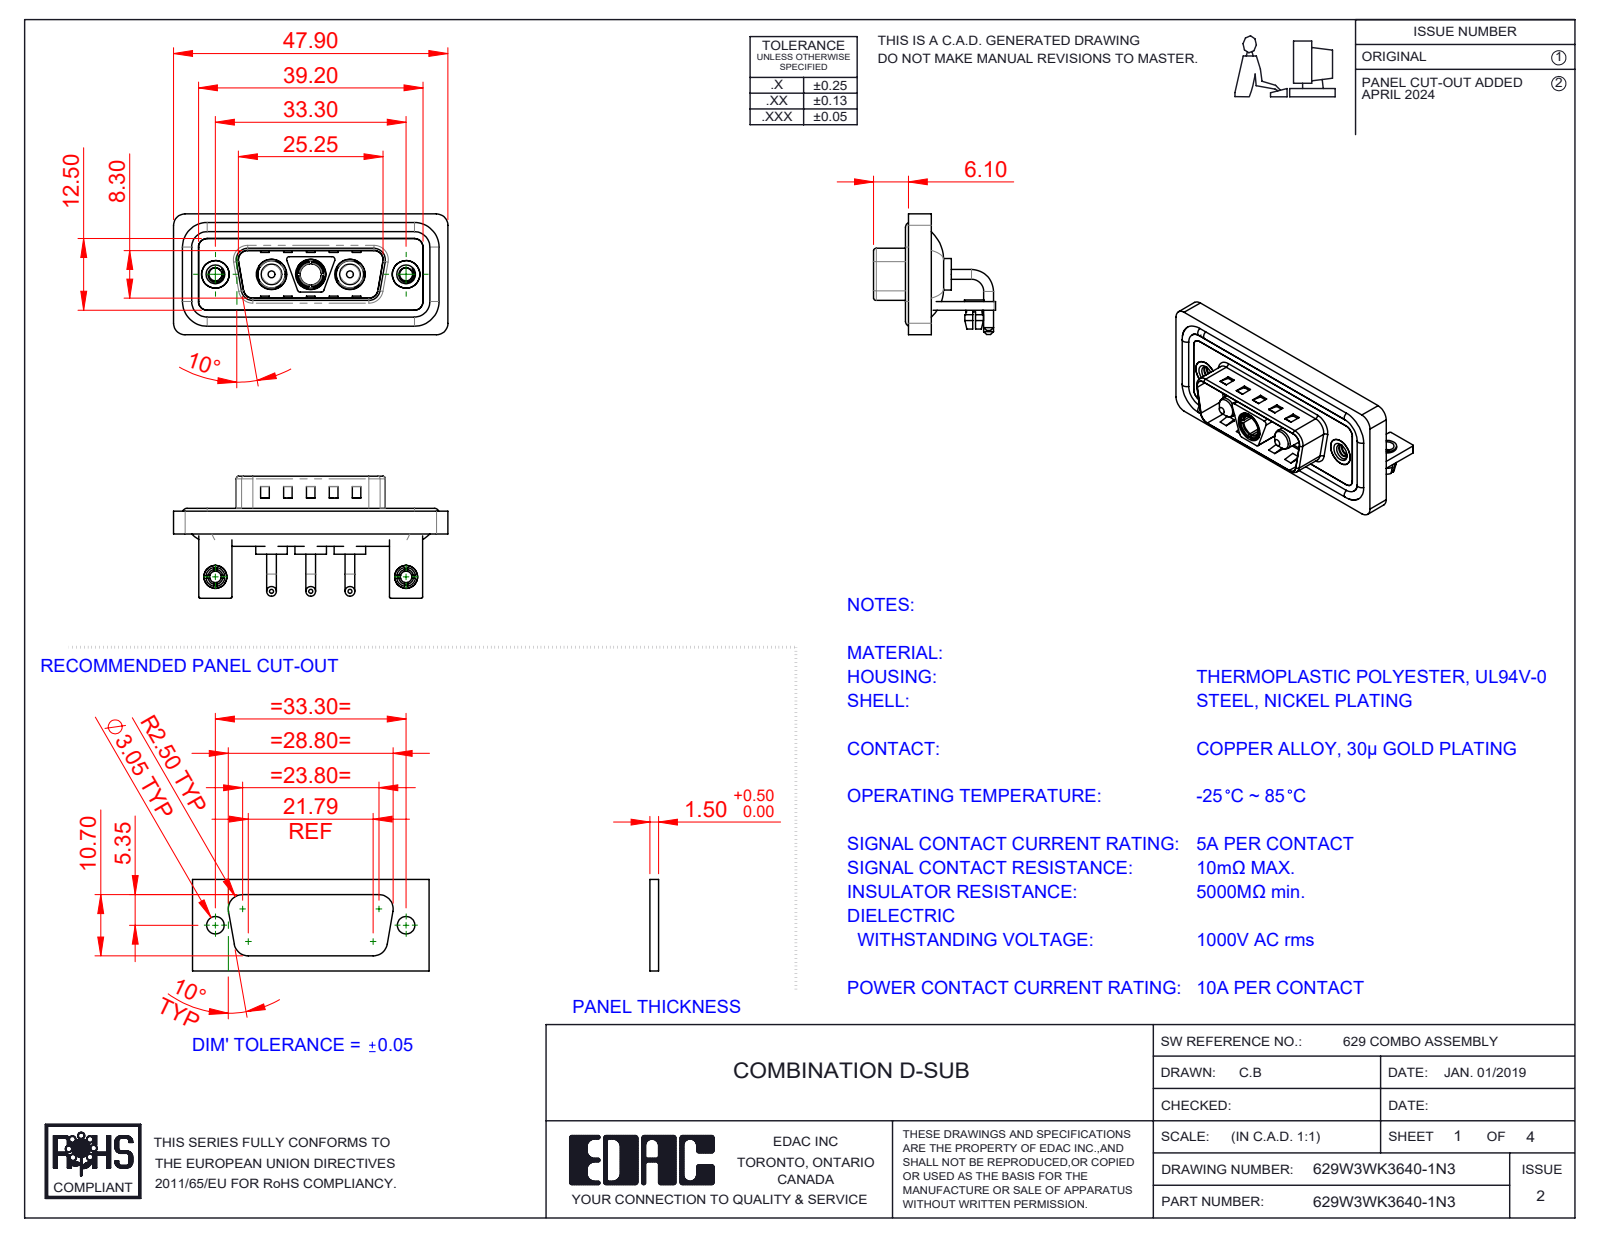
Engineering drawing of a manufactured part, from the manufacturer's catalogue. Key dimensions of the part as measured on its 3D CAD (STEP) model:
Part name (STEP PRODUCT): 629W3WK3640-1N3; Power Pin_10A RA; 629Combo Waterproof Housing_15 Contacts; 629Combo Board Lock (+6 more)
STEP written by: SolidWorks 2023 (CONFIG_CONTROL_DESIGN)
Units: millimetres
Bodies: 17 solids, 753 faces (299 planar, 306 cylindrical, 148 other)
Overall size (bounding box): 47.9 × 21.3 × 21.1
Volume: 6 022 mm³ · Surface area: 10 058 mm²
Round holes (diameter × count): ⌀4.85 ×3, ⌀5.3 ×3, ⌀2 ×2, ⌀2.26 ×2, ⌀2.5 ×2, ⌀3.2 ×2, ⌀4 ×2, ⌀4.8 ×2, ⌀5 ×2, ⌀3.7 ×1
Round bosses / shafts (diameter × count): ⌀1.7 ×6, ⌀1.6 ×4, ⌀5.5 ×3, ⌀5.2 ×3, ⌀4.75 ×3, ⌀3.75 ×3, ⌀4.9 ×2, ⌀4 ×2
Partial cylindrical surfaces — rounded edges, fillets, slot ends (radius × count): R2 ×21, R1.5 ×18, R0.25 ×16, R0.5 ×13, R1.6 ×8, R0.6 ×4, R0.65 ×4, R0.9 ×4
Main face-to-face distances: 0.4, 1.5, 0.8, 2.9, 1.1, 2.1, 3.7, 1.6, 1.2, 4.5
Hole centre spacings: 6.85, 9.8, 16.65, 23.5, 33.3, 13.7
